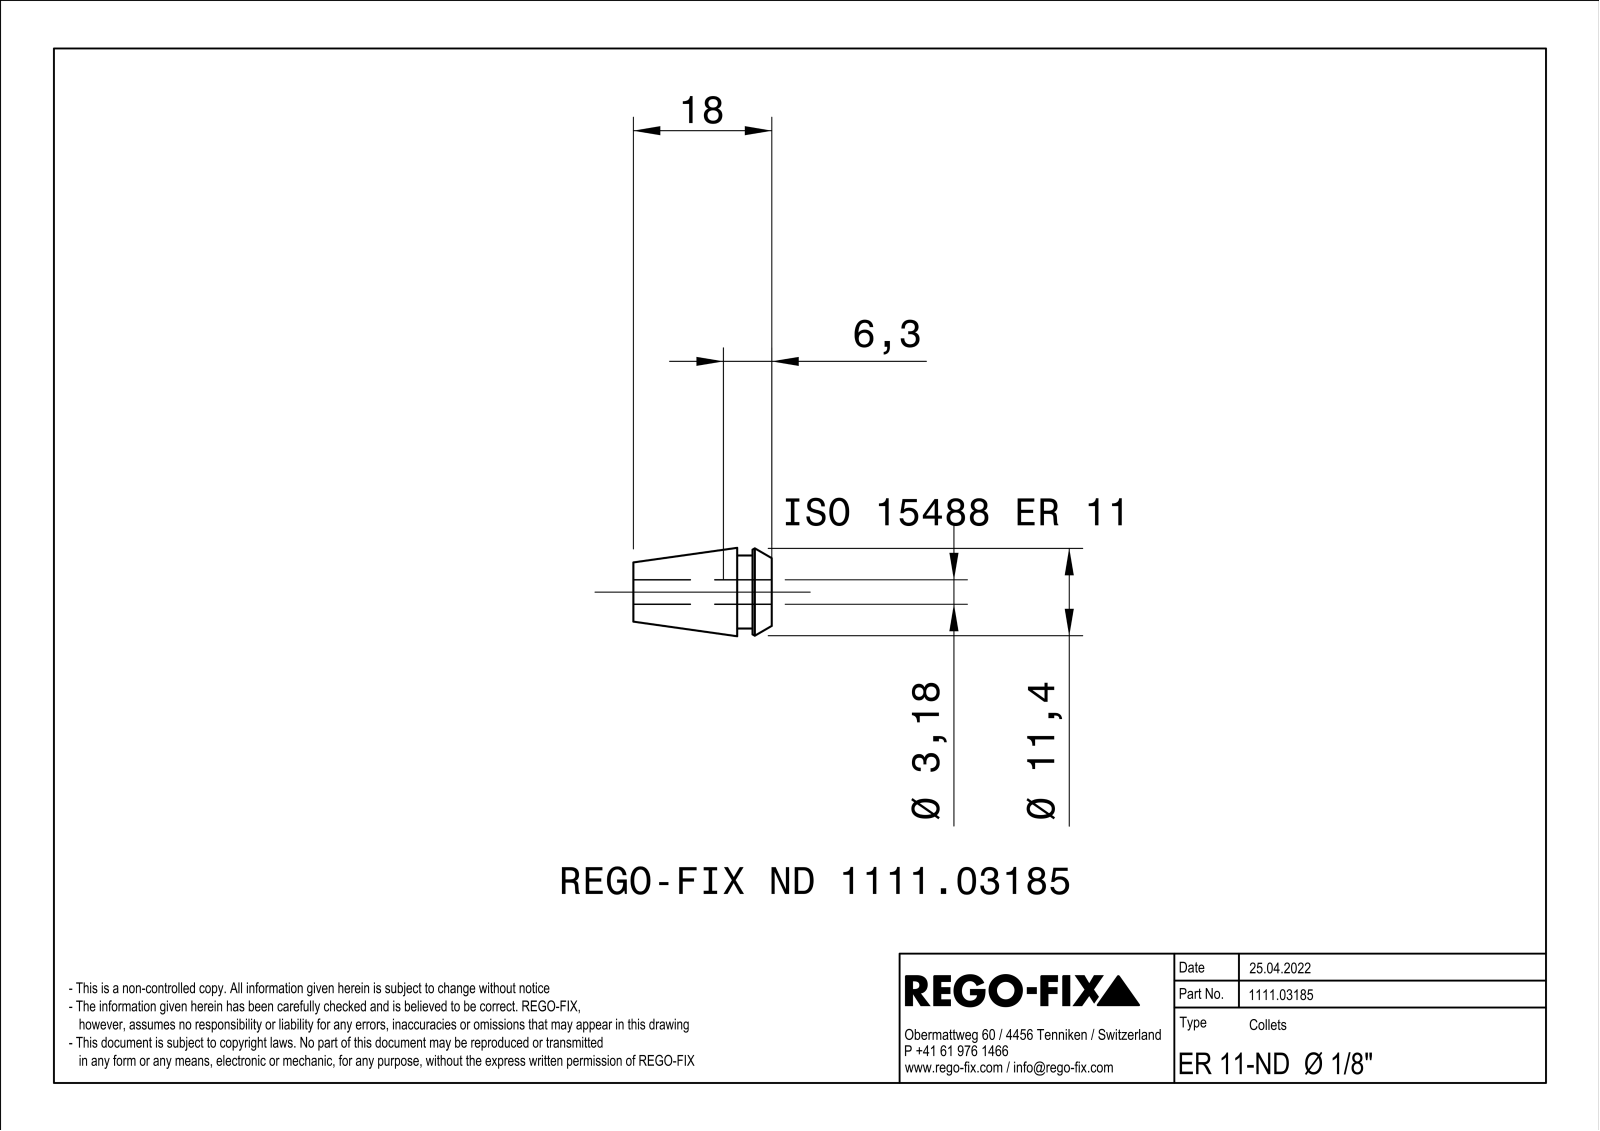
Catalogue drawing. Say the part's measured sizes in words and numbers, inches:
The part is named "NOCUT". Its 3-D file was written by "SIEMENS PLM Software Solid Edge ST10 (AUTOMOTIVE_DESIGN)". It is 1 solid with 54 faces: 25 planar, 5 cylindrical and 24 other. Overall it measures 0.709 by 0.453 by 0.453 inches. Its volume is 0.061 cubic inches and its surface area 1.834 square inches. Round holes: 1 of diameter 0.125. Round bosses or shafts: 1 of diameter 0.374. The main face-to-face distances are 0.017, 0.098, 0.709, 0.61, 0.177, 0.079, 0.531, 0.591, 0.492, 0.413.
